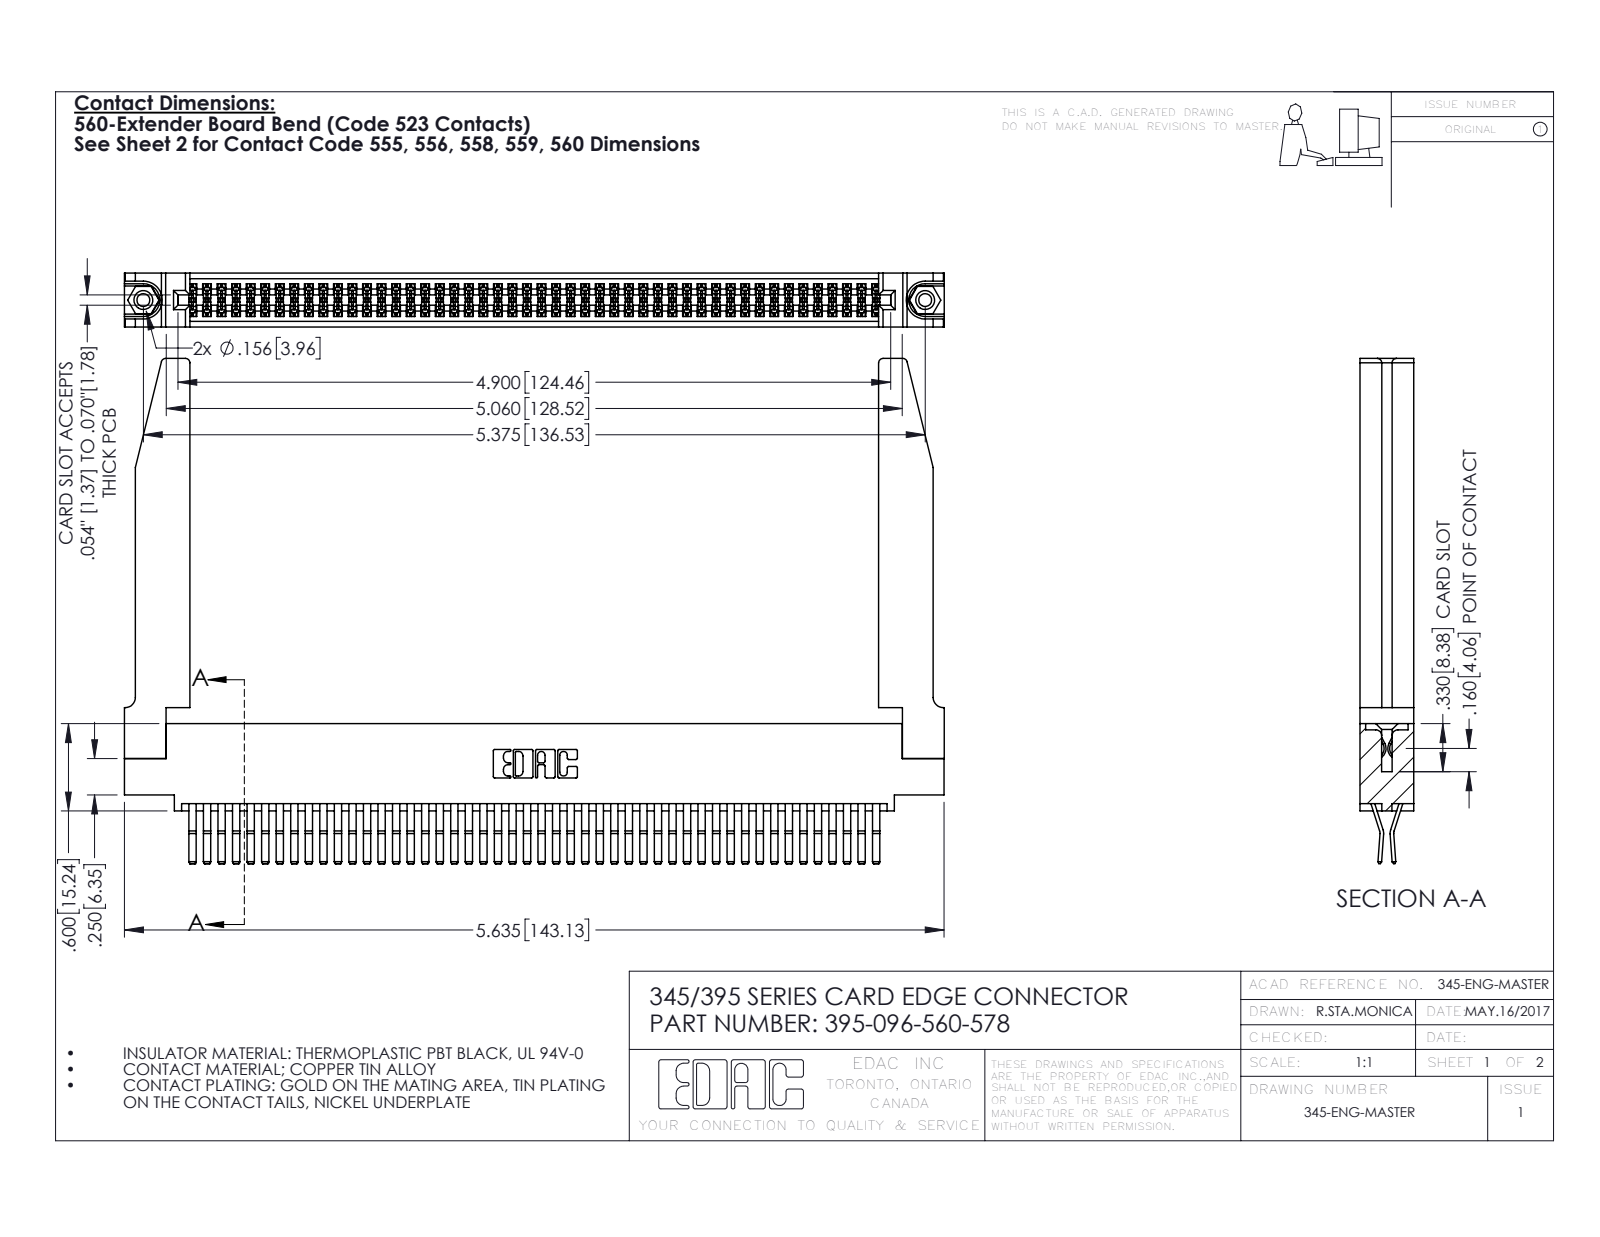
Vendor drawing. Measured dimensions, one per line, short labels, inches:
name: 345-250-001_345-250-001-102; 345 Part_0.110 Offset - 0.156 Dia-TH; 395-096-560-578; 345-220-078_345-220-078 (+1 more)
written by: SolidWorks 2016 (CONFIG_CONTROL_DESIGN)
unit: in
bodies: 101 solids, 5356 faces (3394 planar, 1910 cylindrical, 52 other)
size: 5.636 × 3.472 × 0.37
volume: 1.36 in³; area: 46.69 in²
holes: 2× ⌀0.089, 2× ⌀0.125, 2× ⌀0.156, 1× ⌀0.064
bosses: 2× ⌀0.155
rounds: 145× R0.006, 22× R0.01, 8× R0.03, 6× R0.007, 6× R0.031, 3× R0.026, 2× R0.01, 2× R0.014
face distances: 0.072, 0.37, 0.298, 0.025, 0.098, 0.272, 0.2, 0.225, 0.15, 0.148
hole spacings: 0.27, 5.139, 5.375
